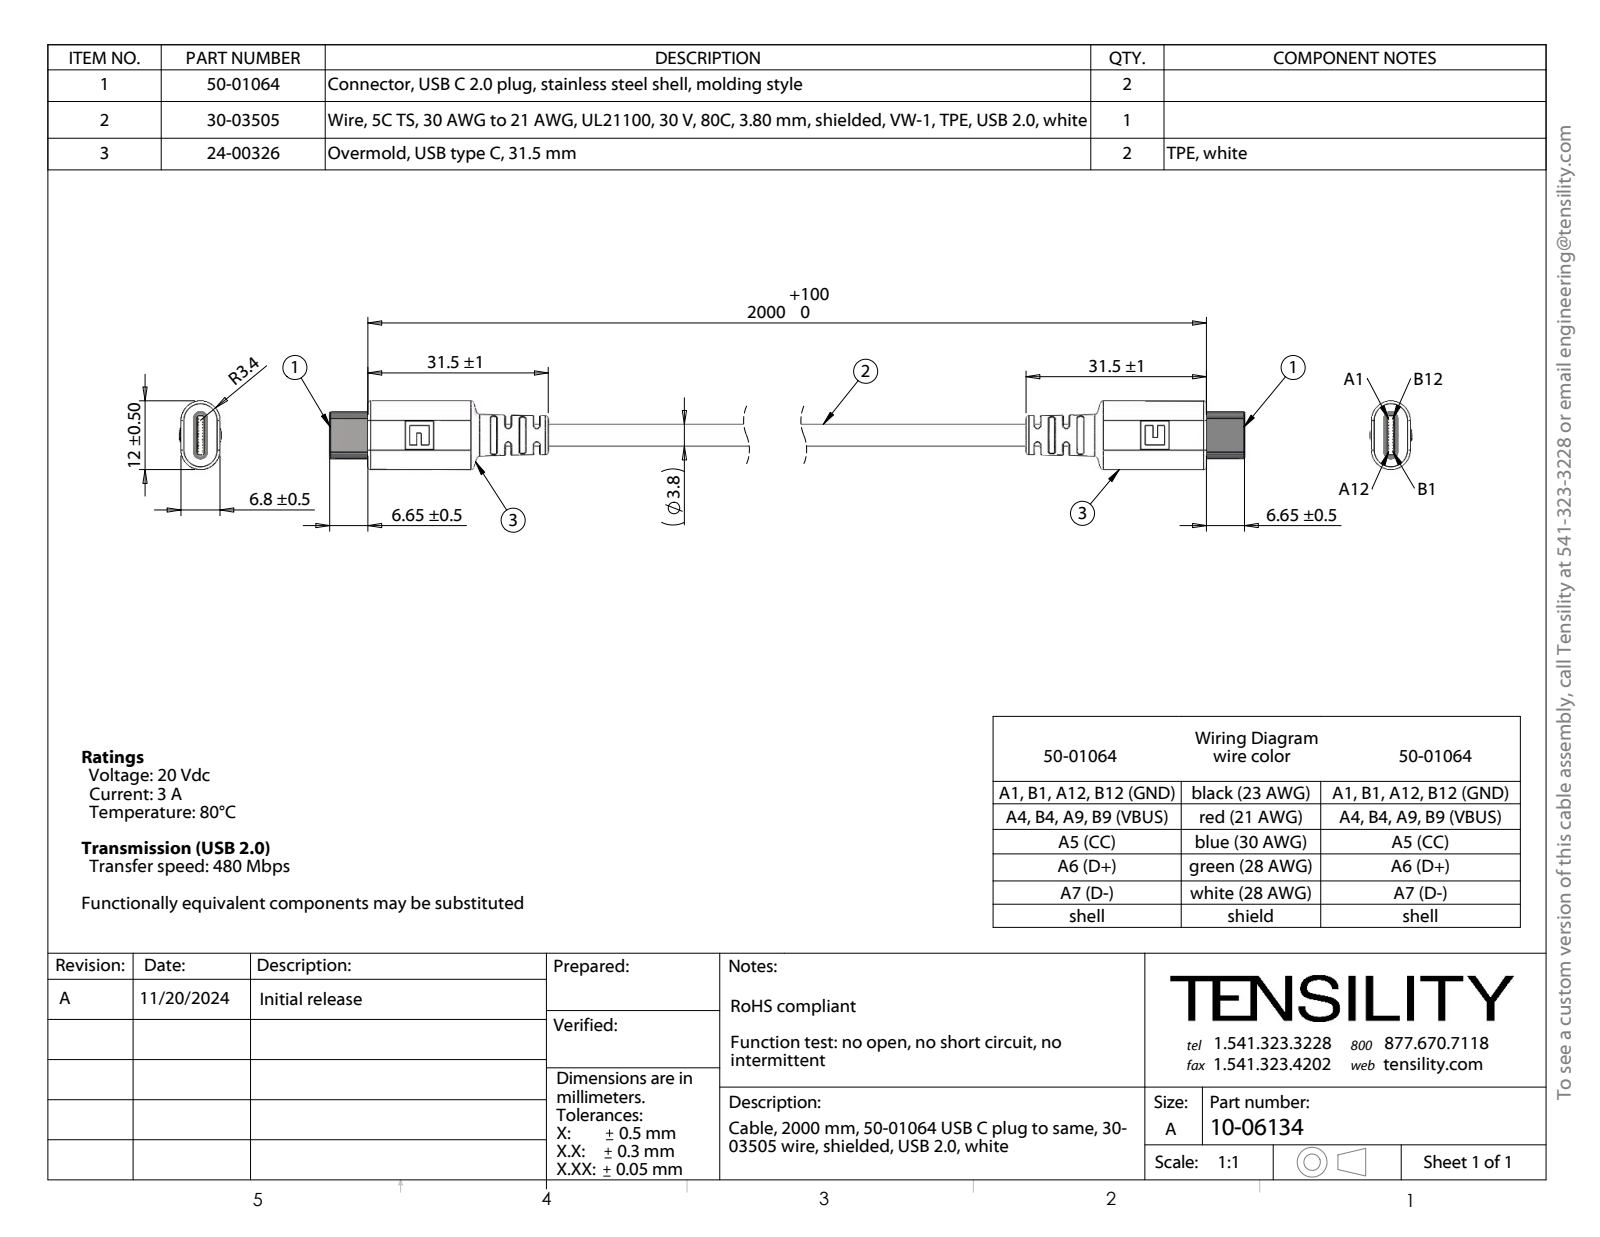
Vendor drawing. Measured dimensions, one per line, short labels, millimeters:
name: 30-03505_blunt cut; 10-06134; 24-00326; 50-01064_Hidden emarker
written by: SolidWorks 2021 (CONFIG_CONTROL_DESIGN)
unit: mm
bodies: 55 solids, 1076 faces (496 planar, 352 cylindrical, 228 other)
size: 206.3 × 12 × 7.38
volume: 5 080 mm³; area: 20 593 mm²
holes: 1× ⌀2.73, 1× ⌀2.76, 1× ⌀2.98
bosses: 2× ⌀0.83, 1× ⌀3.8, 1× ⌀2.96, 1× ⌀2.75, 1× ⌀1.2, 1× ⌀1, 1× ⌀0.55
rounds: 20× R0.5, 4× R0.1, 4× R0.15, 4× R0.25, 2× R0.6, 2× R1.18, 2× R3.4
face distances: 6.8, 2.5, 2.35, 1.7, 2.23, 4.57, 4.58, 2.22, 0.65, 1
hole spacings: 0.43, 0.32, 0.33, 0.49, 0.42, 0.59, 0.56, 0.58
